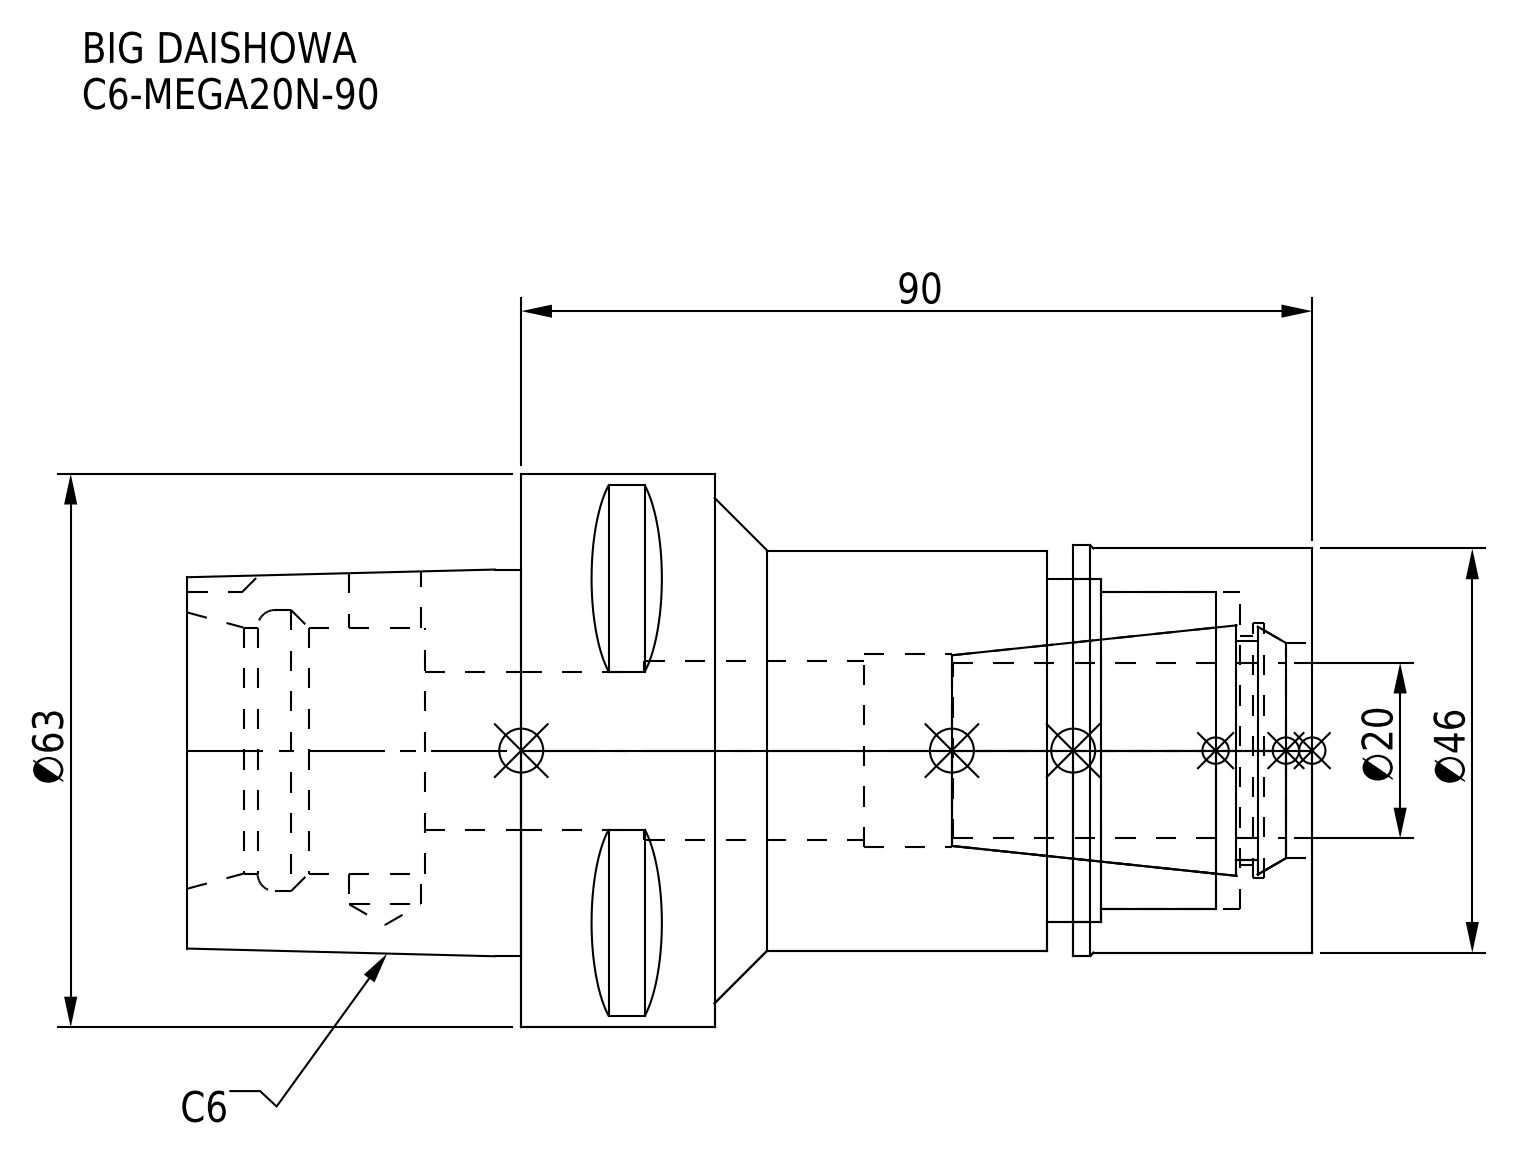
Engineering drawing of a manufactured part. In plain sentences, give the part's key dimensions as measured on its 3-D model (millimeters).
The part is named "DXF_TEMP_ASSY_ASM_4_ASM.stp; C6-MEGA20N-90-200.stp; C6-MEGA20N-90-200_ASM.stp; C6-MEGA20N-90_1.stp (+3 more)". Its 3-D file was written by "SolidWorks 2019 (CONFIG_CONTROL_DESIGN)". It is 2 solids with 95 faces: 38 planar, 39 cylindrical and 18 other. Overall it measures 128 by 63 by 63 millimeters. Its volume is 176 542 cubic millimeters and its surface area 40 517 square millimeters. Round holes: 1 of diameter 8.1, 1 of diameter 18, 1 of diameter 20.3, 1 of diameter 22, 1 of diameter 24.5, 1 of diameter 26, 1 of diameter 28, 1 of diameter 29, 1 of diameter 32, 1 of diameter 36, 1 of diameter 39. Round bosses or shafts: 1 of diameter 63, 1 of diameter 46.7, 1 of diameter 46, 1 of diameter 45.5. Partial cylindrical surfaces (rounded edges, fillets, slot ends): 1 of radius 5. The main face-to-face distances are 90, 22, 59.8, 11, 68, 27.2, 40.8, 62.8, 60, 128.
